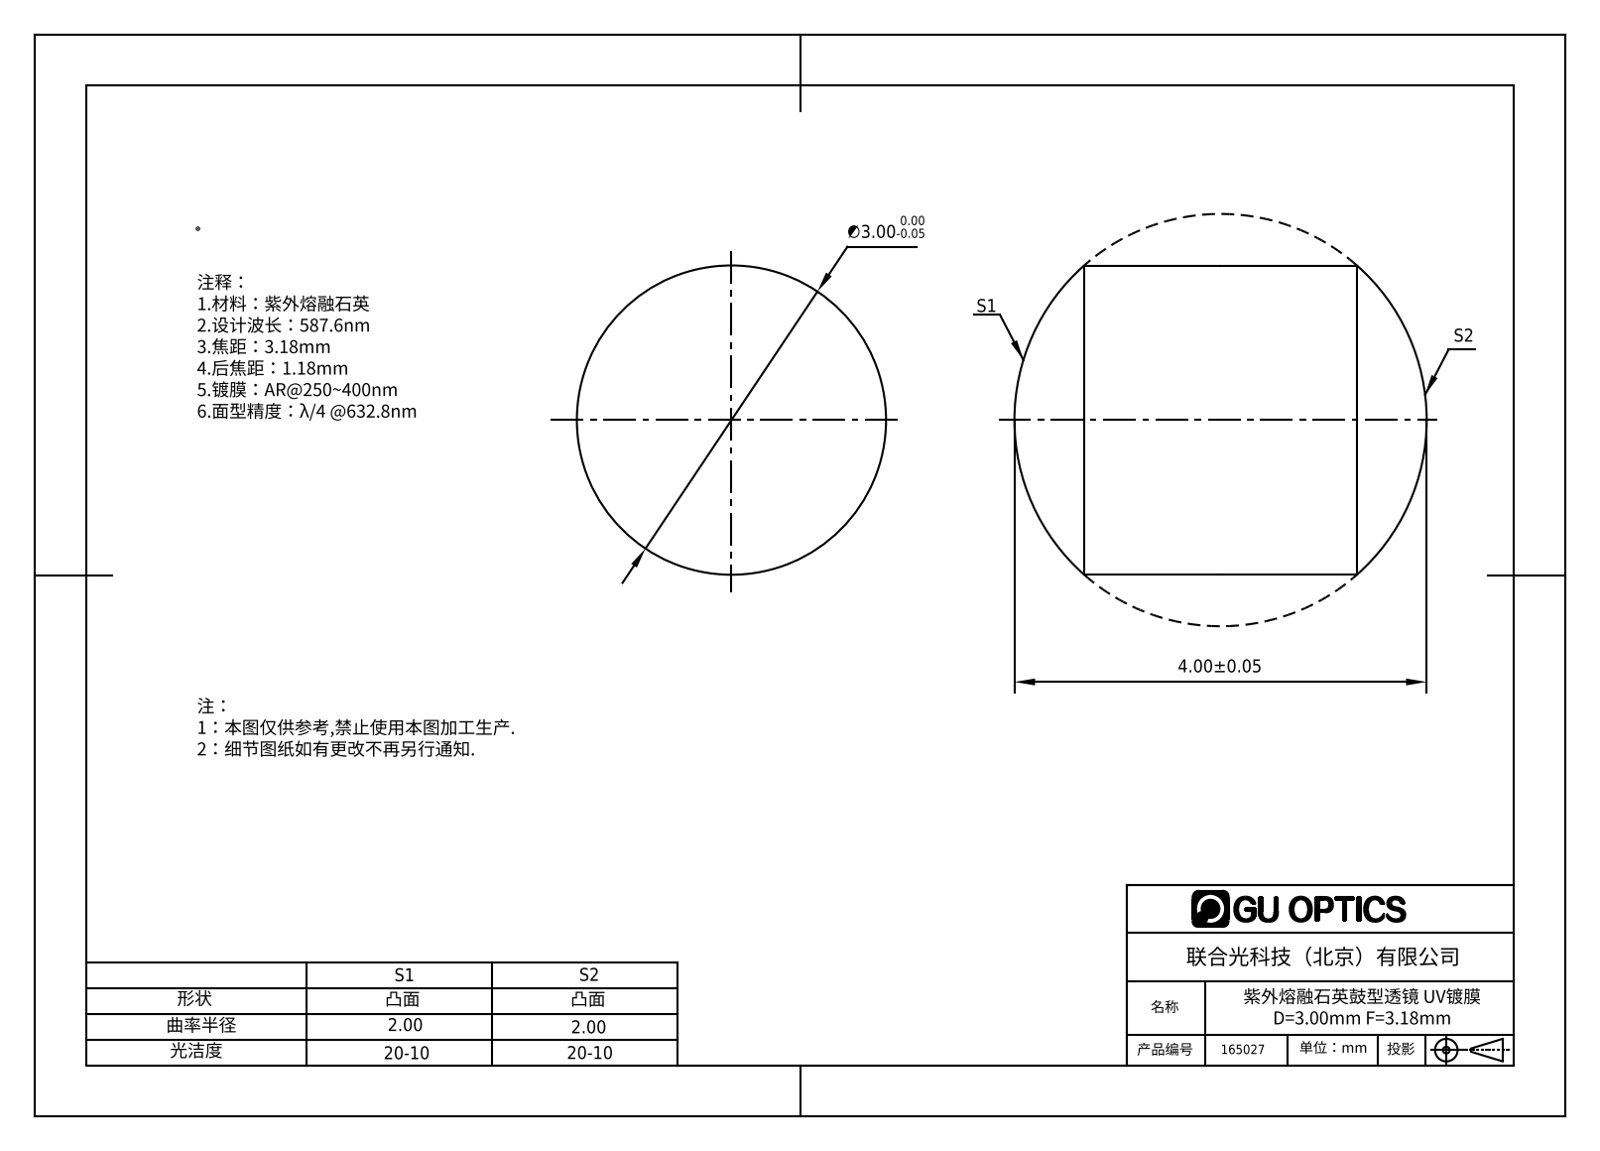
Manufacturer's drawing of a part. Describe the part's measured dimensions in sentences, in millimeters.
The part is named "165002". Its 3-D file was written by "SolidWorks 2016 (CONFIG_CONTROL_DESIGN)". It is 1 solid with 6 faces: 0 planar, 2 cylindrical and 4 other. Overall it measures 4 by 3 by 3 millimeters. Its volume is 24 cubic millimeters and its surface area 42 square millimeters. Round bosses or shafts: 1 of diameter 3.
